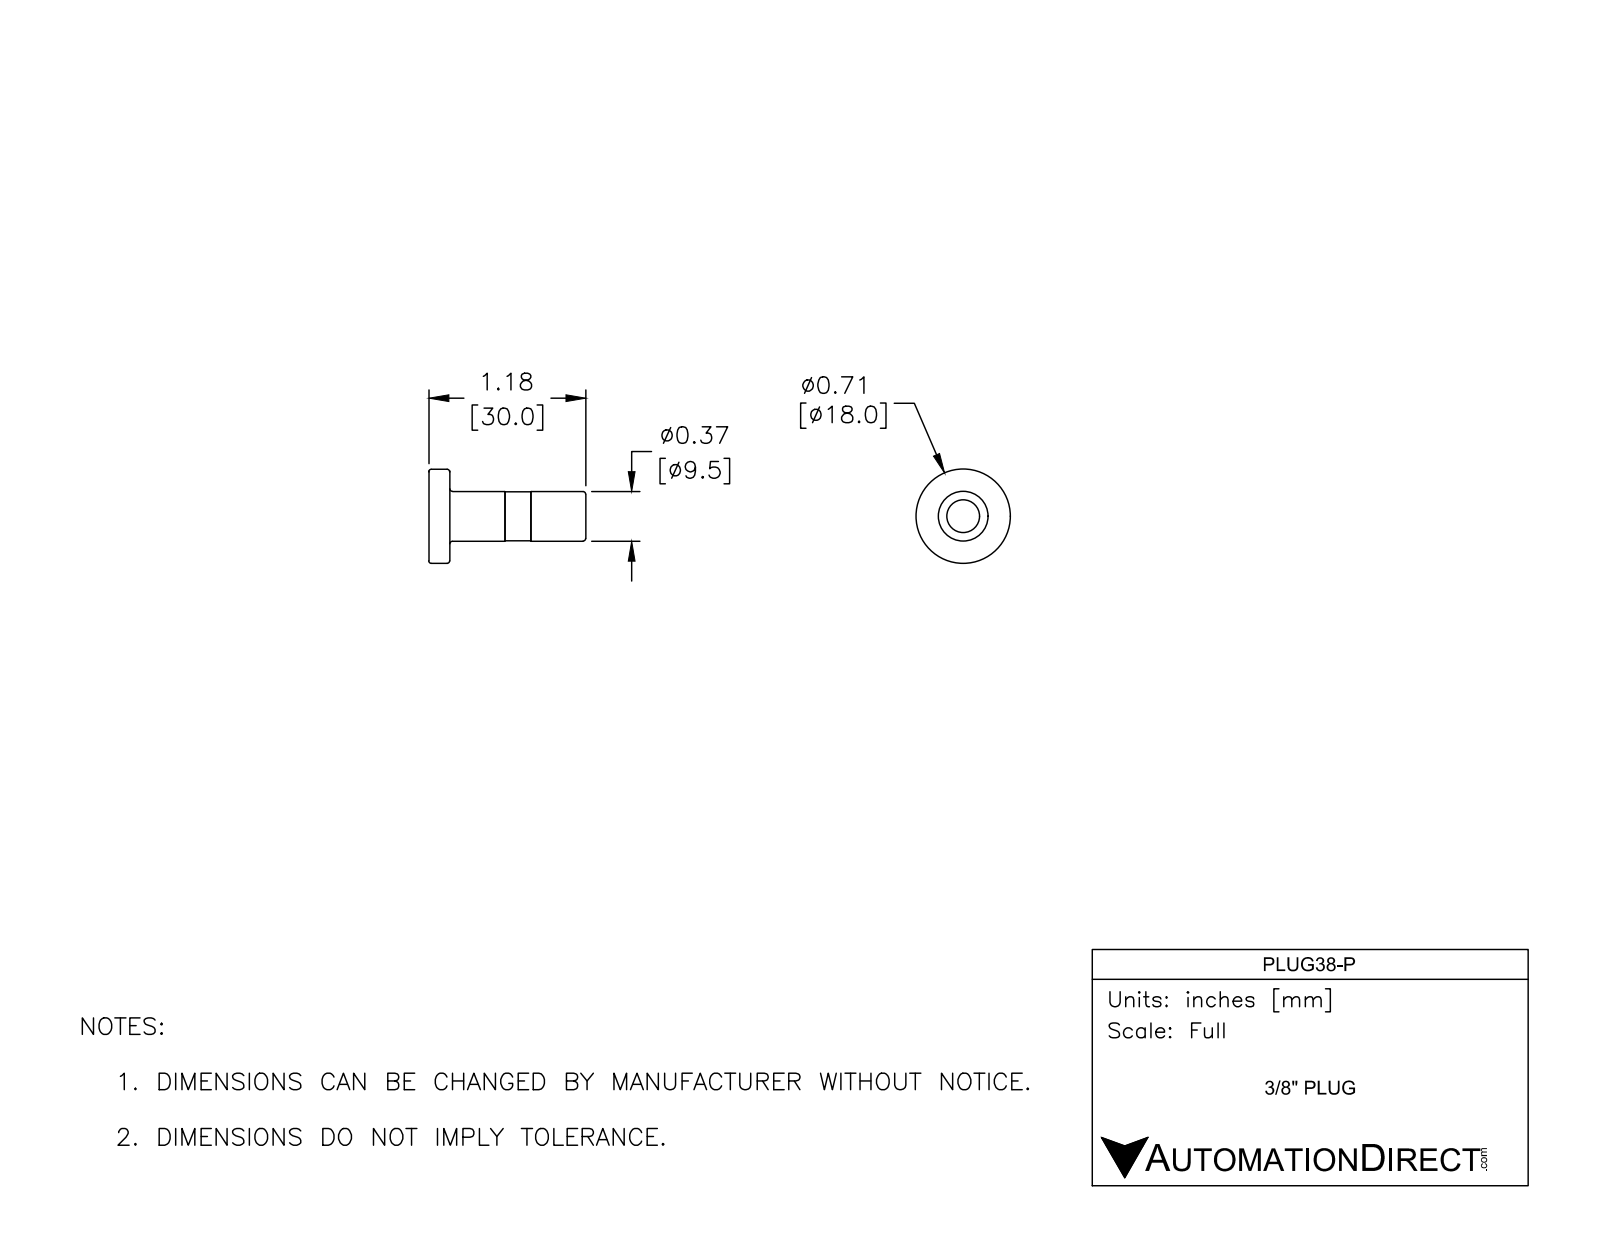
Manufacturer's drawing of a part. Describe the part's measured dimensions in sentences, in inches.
The part is named "PLUG38-P". Its 3-D file was written by "SolidWorks 2017 (AUTOMOTIVE_DESIGN)". It is 1 solid with 38 faces: 6 planar, 12 cylindrical and 20 other. Overall it measures 1.181 by 0.709 by 0.709 inches. Its volume is 0.114 cubic inches and its surface area 3.114 square inches. Round holes: 1 of diameter 0.248. Round bosses or shafts: 1 of diameter 0.709, 1 of diameter 0.374, 1 of diameter 0.368. The main face-to-face distances are 0.138, 0.02, 0.157, 1.181, 1.161, 1.024, 0.563, 0.543, 0.406, 0.618.
